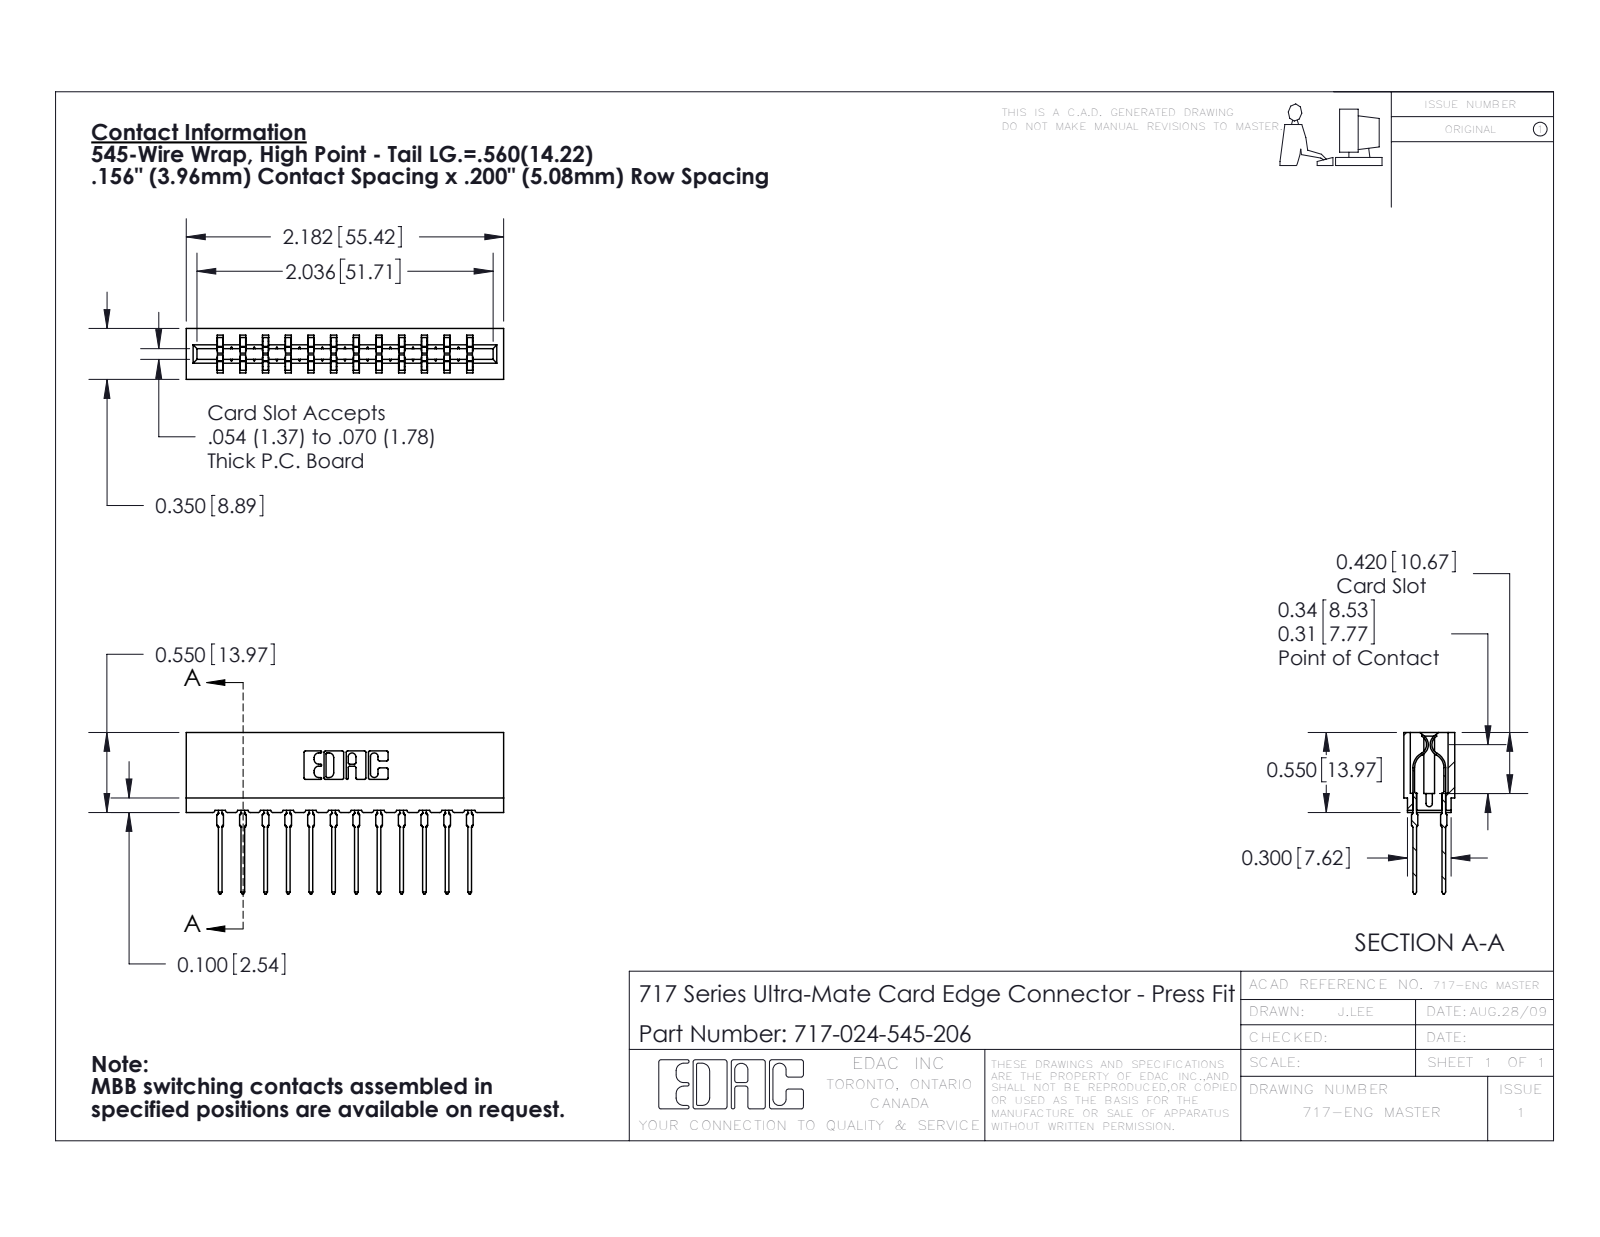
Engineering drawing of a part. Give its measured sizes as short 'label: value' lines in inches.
name: 717 Part_Insulator Option - 06; 717-024-545-206; 745-292-001_545
written by: SolidWorks 2016 (CONFIG_CONTROL_DESIGN)
unit: in
bodies: 25 solids, 2254 faces (1170 planar, 460 cylindrical, 624 other)
size: 2.182 × 1.109 × 0.35
volume: 0.306 in³; area: 11.89 in²
rounds: 48× R0.021, 24× R0.015, 22× R0.01, 8× R0.005, 8× R0.011, 6× R0.007, 6× R0.031, 3× R0.026
face distances: 0.212, 0.138, 0.156, 0.624, 0.35, 0.468, 0.063, 0.287, 0.076, 0.149
